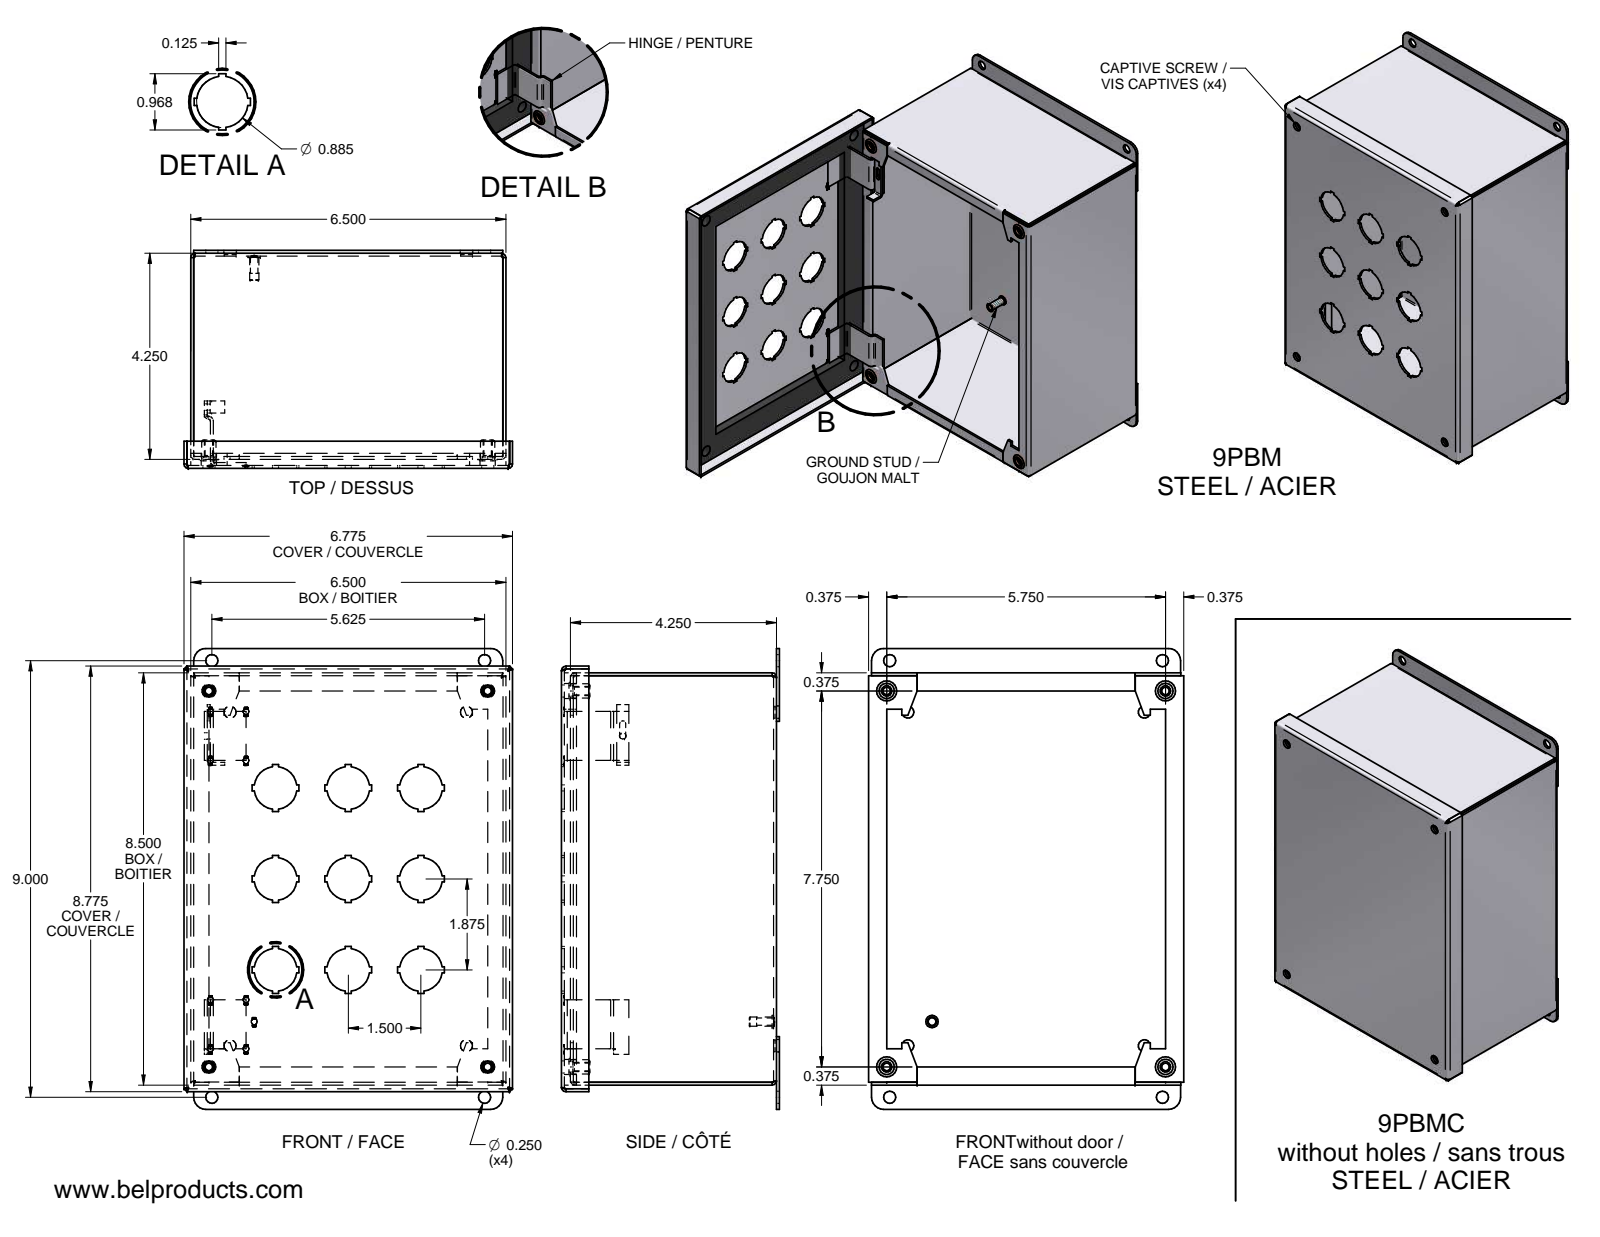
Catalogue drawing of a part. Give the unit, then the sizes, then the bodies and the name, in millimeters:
Units: millimetres
Overall size (bounding box): 241.3 × 172.09 × 114.17
Round holes (diameter × count): ⌀3.17 ×9, ⌀6.35 ×8, ⌀4.04 ×4, ⌀5.49 ×4, ⌀6.22 ×4, ⌀6.73 ×4, ⌀7.37 ×4, ⌀7.92 ×4, ⌀3.45 ×1
Round bosses / shafts (diameter × count): ⌀3.02 ×9, ⌀7.52 ×4, ⌀6.35 ×4, ⌀6.5 ×1, ⌀4.83 ×1, ⌀0.51 ×1
Partial cylindrical surfaces — rounded edges, fillets, slot ends (radius × count): R0.81 ×16, R2.34 ×16, R6.35 ×4, R1.59 ×2
Main face-to-face distances: 1.52, 112.65, 111.13, 163.58, 1.53, 111.12, 109.6, 214.38, 165.1, 162.06
Hole centre spacings: 135.4, 145.34, 146.06, 15.72, 15.96, 18.7, 25.65, 28.62
Volume: 362 443 mm³ · Surface area: 410 382 mm²
Bodies: 13 solids, 1286 faces (899 planar, 106 cylindrical, 281 other)
Part name (STEP PRODUCT): 9PBMC_COUVERCLE; 9PBMC-C; 9PBMC_GASKET; PB-PENTURE-1 (+7 more)
STEP written by: Unknown (AUTOMOTIVE_DESIGN)
